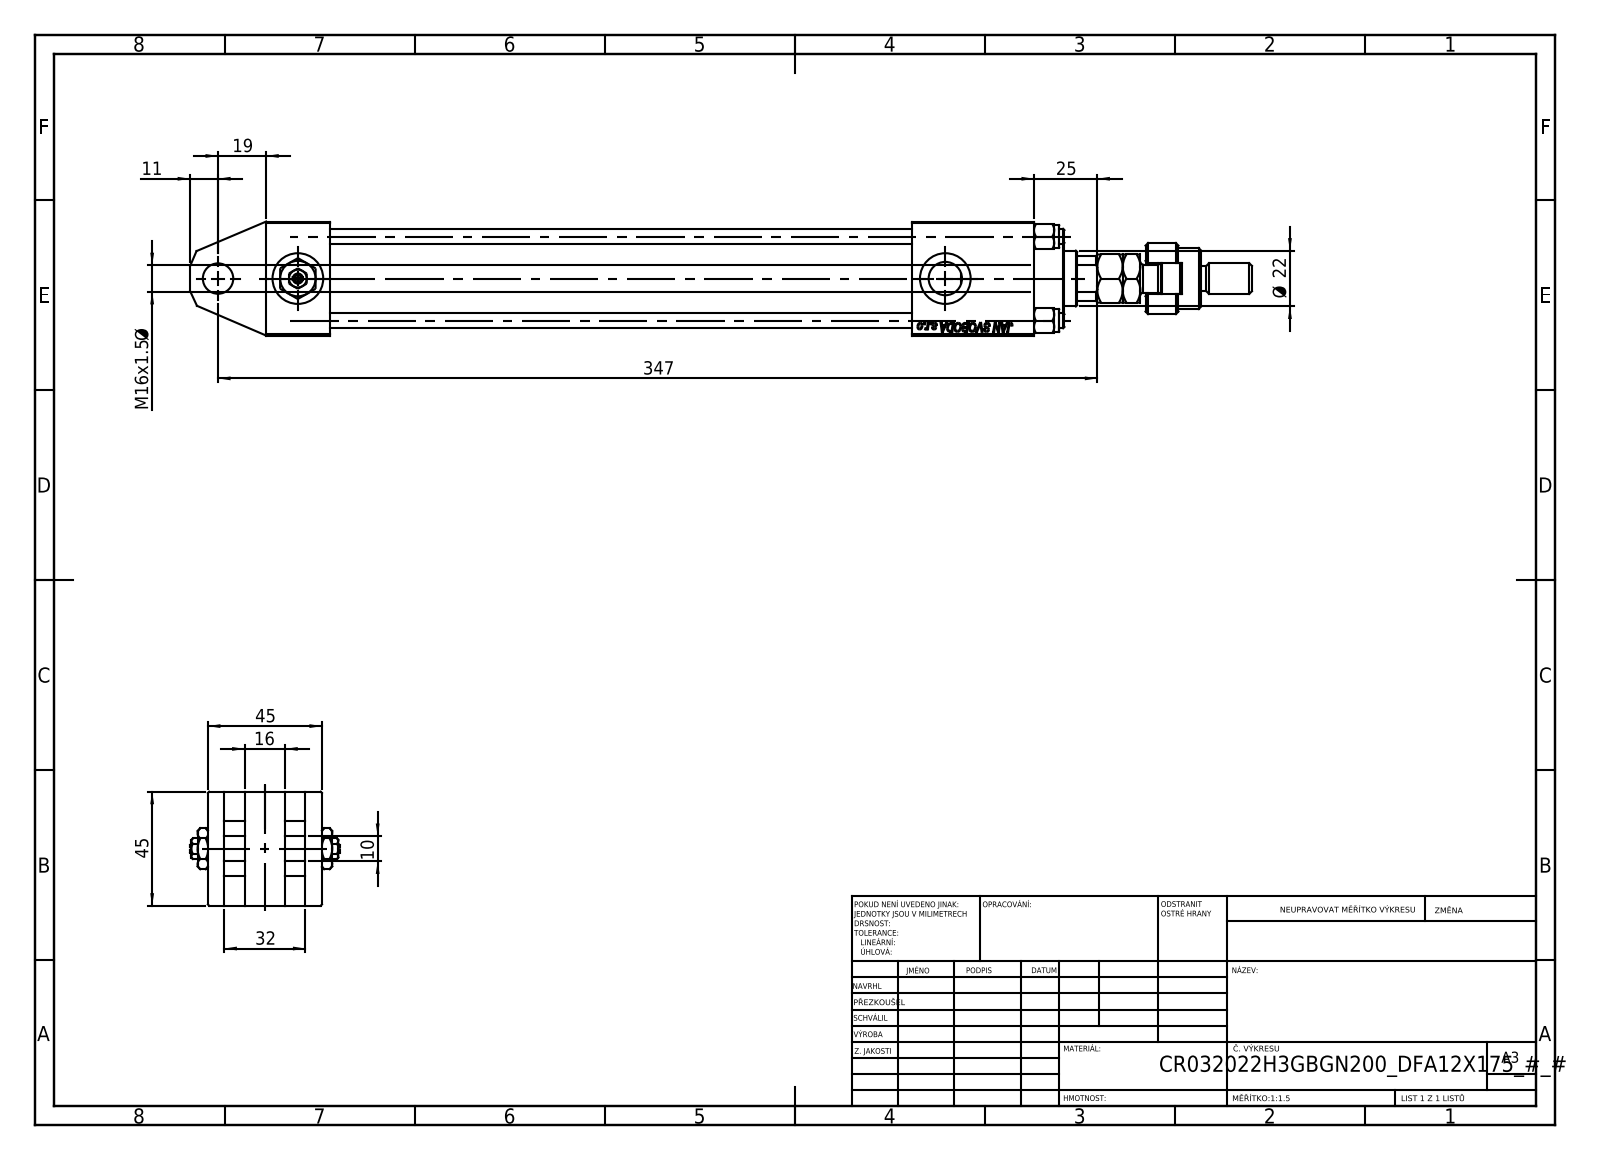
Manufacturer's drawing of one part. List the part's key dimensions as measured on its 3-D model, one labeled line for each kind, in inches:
Part name (STEP PRODUCT): V215CR_TYCINKA_H; Zatka_pro_OIL_PORT; V215CR_VCP_H; MFA (+4 more)
STEP written by: SolidWorks 2019 (CONFIG_CONTROL_DESIGN)
Units: inches
Bodies: 15 solids, 1313 faces (592 planar, 107 cylindrical, 614 other)
Overall size (bounding box): 16.496 × 2.323 × 1.772
Volume: 23.76 in³ · Surface area: 237.1 in²
Round holes (diameter × count): ⌀0.236 ×4, ⌀0.276 ×2, ⌀0.518 ×2, ⌀0.787 ×2, ⌀0.413 ×1, ⌀0.472 ×1, ⌀0.866 ×1, ⌀0.945 ×1, ⌀0.984 ×1, ⌀1.26 ×1, ⌀1.299 ×1
Round bosses / shafts (diameter × count): ⌀0.354 ×4, ⌀1.496 ×1, ⌀1.339 ×1, ⌀1.102 ×1, ⌀0.709 ×1, ⌀0.472 ×1, ⌀0.433 ×1, ⌀0.394 ×1
Partial cylindrical surfaces — rounded edges, fillets, slot ends (radius × count): R0.384 ×1, R0.413 ×1
Main face-to-face distances: 1.772, 0.315, 0.984, 0.571, 1.516, 0.945, 1.201, 0.256, 11.929, 1.26
Hole centre spacings: 0.924, 1.307, 1.848, 1.24, 10.059, 11.299
